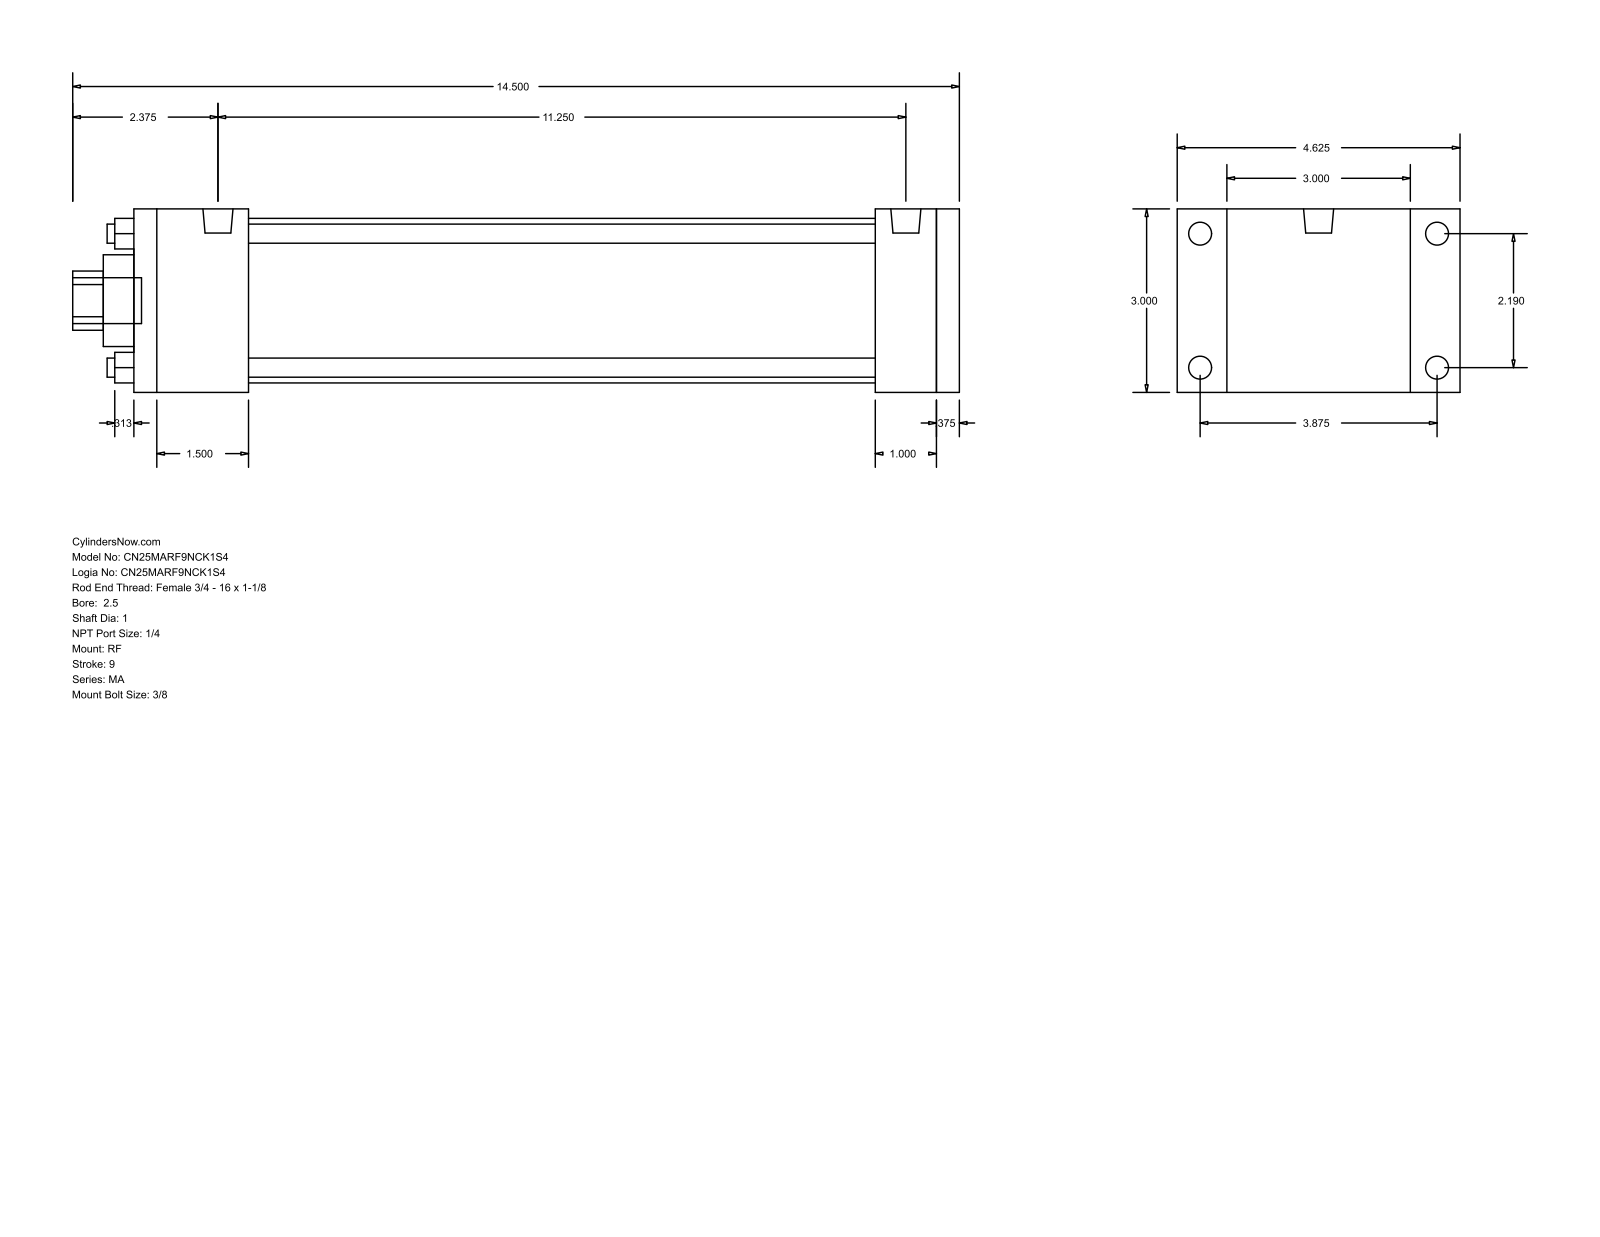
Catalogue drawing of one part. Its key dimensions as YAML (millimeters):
part_name: "MA_RF__0250_1"
step_written_by: "GSSL Pune (CONFIG_CONTROL_DESIGN)"
units: millimeters
bodies: {solids: 0, faces: 92, planar: 64, cylindrical: 28, other: 0}
overall_size: [368.3, 117.47, 76.2]
round_holes:
  - {diameter: 7.94, count: 4}
  - {diameter: 25.4, count: 1}
  - {diameter: 38.1, count: 1}
  - {diameter: 68.33, count: 1}
round_bosses_or_shafts:
  - {diameter: 9.53, count: 4}
  - {diameter: 7.94, count: 4}
  - {diameter: 12.49, count: 2}
  - {diameter: 19.05, count: 1}
partial_cylinders:
  - {radius: 12.29, count: 1}
face_to_face_distances: [76.2, 342.9, 9.53, 333.37, 47.63, 307.98, 260.35, 285.74, 295.27, 25.39]
hole_center_spacings: [39.33, 55.62, 78.66]
